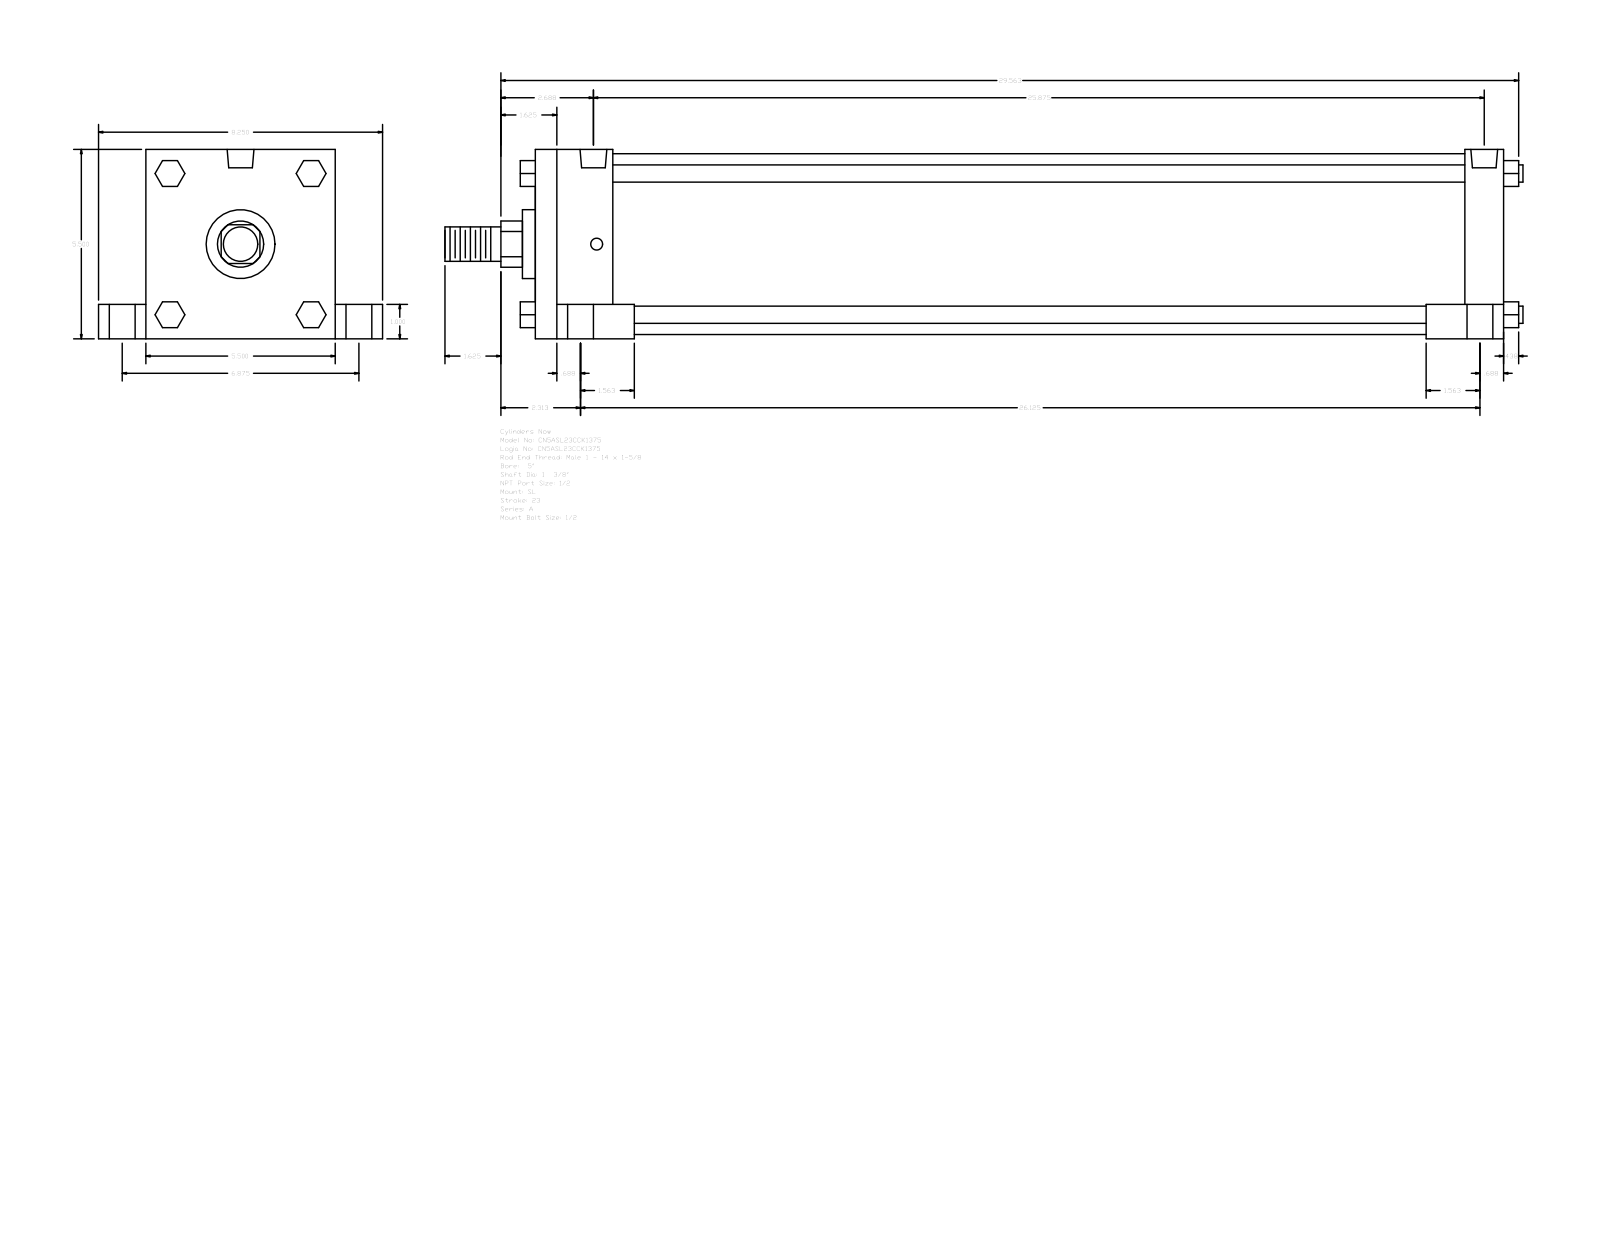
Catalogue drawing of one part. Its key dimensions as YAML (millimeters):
part_name: "A_SL__0500_1.375"
step_written_by: "GSSL Pune (CONFIG_CONTROL_DESIGN)"
units: millimeters
bodies: {solids: 0, faces: 150, planar: 114, cylindrical: 36, other: 0}
overall_size: [795.34, 209.55, 139.7]
round_holes:
  - {diameter: 8.73, count: 4}
  - {diameter: 19.05, count: 4}
  - {diameter: 25.4, count: 4}
  - {diameter: 19.77, count: 2}
round_bosses_or_shafts:
  - {diameter: 12.7, count: 4}
  - {diameter: 133.35, count: 1}
  - {diameter: 50.8, count: 1}
  - {diameter: 34.92, count: 1}
  - {diameter: 25.4, count: 1}
partial_cylinders:
  - {radius: 17.06, count: 1}
face_to_face_distances: [139.7, 714.37, 57.15, 657.22, 25.4, 114.3, 34.93, 174.63, 28.57, 685.8]
hole_center_spacings: [2.39, 87.31, 87.37, 87.83, 88.12, 174.62, 652.45, 654.84]
